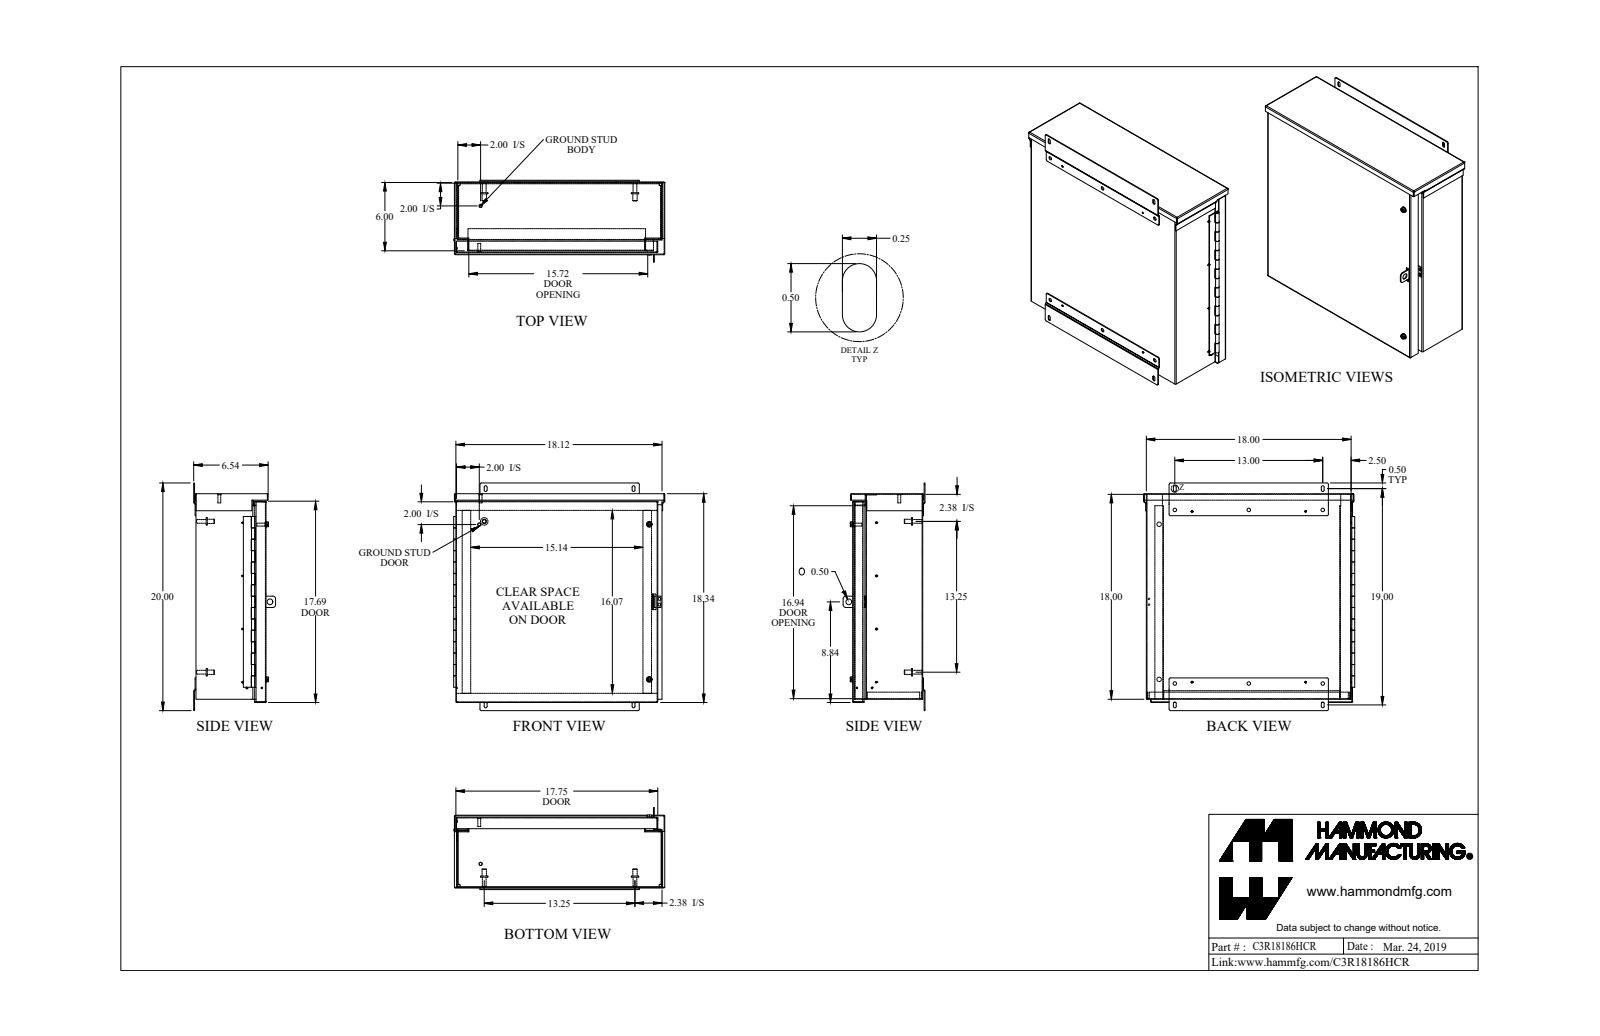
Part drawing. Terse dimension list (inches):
name: C3R18186HCR_Default
written by: SolidWorks 2019 (CONFIG_CONTROL_DESIGN)
unit: in
bodies: 33 solids, 846 faces (481 planar, 311 cylindrical, 54 other)
size: 20 × 18.556 × 7.197
volume: 92.43 in³; area: 3 001 in²
holes: 9× ⌀0.313, 4× ⌀0.14, 3× ⌀0.26, 2× ⌀0.137, 2× ⌀0.266, 2× ⌀0.28, 2× ⌀0.29, 2× ⌀0.397, 1× ⌀0.188, 1× ⌀0.5
bosses: 10× ⌀0.131, 4× ⌀0.65, 4× ⌀0.375, 4× ⌀0.33, 3× ⌀0.51, 3× ⌀0.244, 3× ⌀0.187, 2× ⌀0.5
rounds: 26× R0.029, 26× R0.086, 19× R0.125, 5× R0.036, 5× R0.108, 3× R0.171, 2× R0.25
face distances: 0.057, 6.1, 6.043, 6.157, 18, 17.943, 0.943, 18.057, 4.943, 17.886
hole spacings: 1.505, 5.002, 6.5, 11.501, 15.93, 19, 15.199, 16.577
